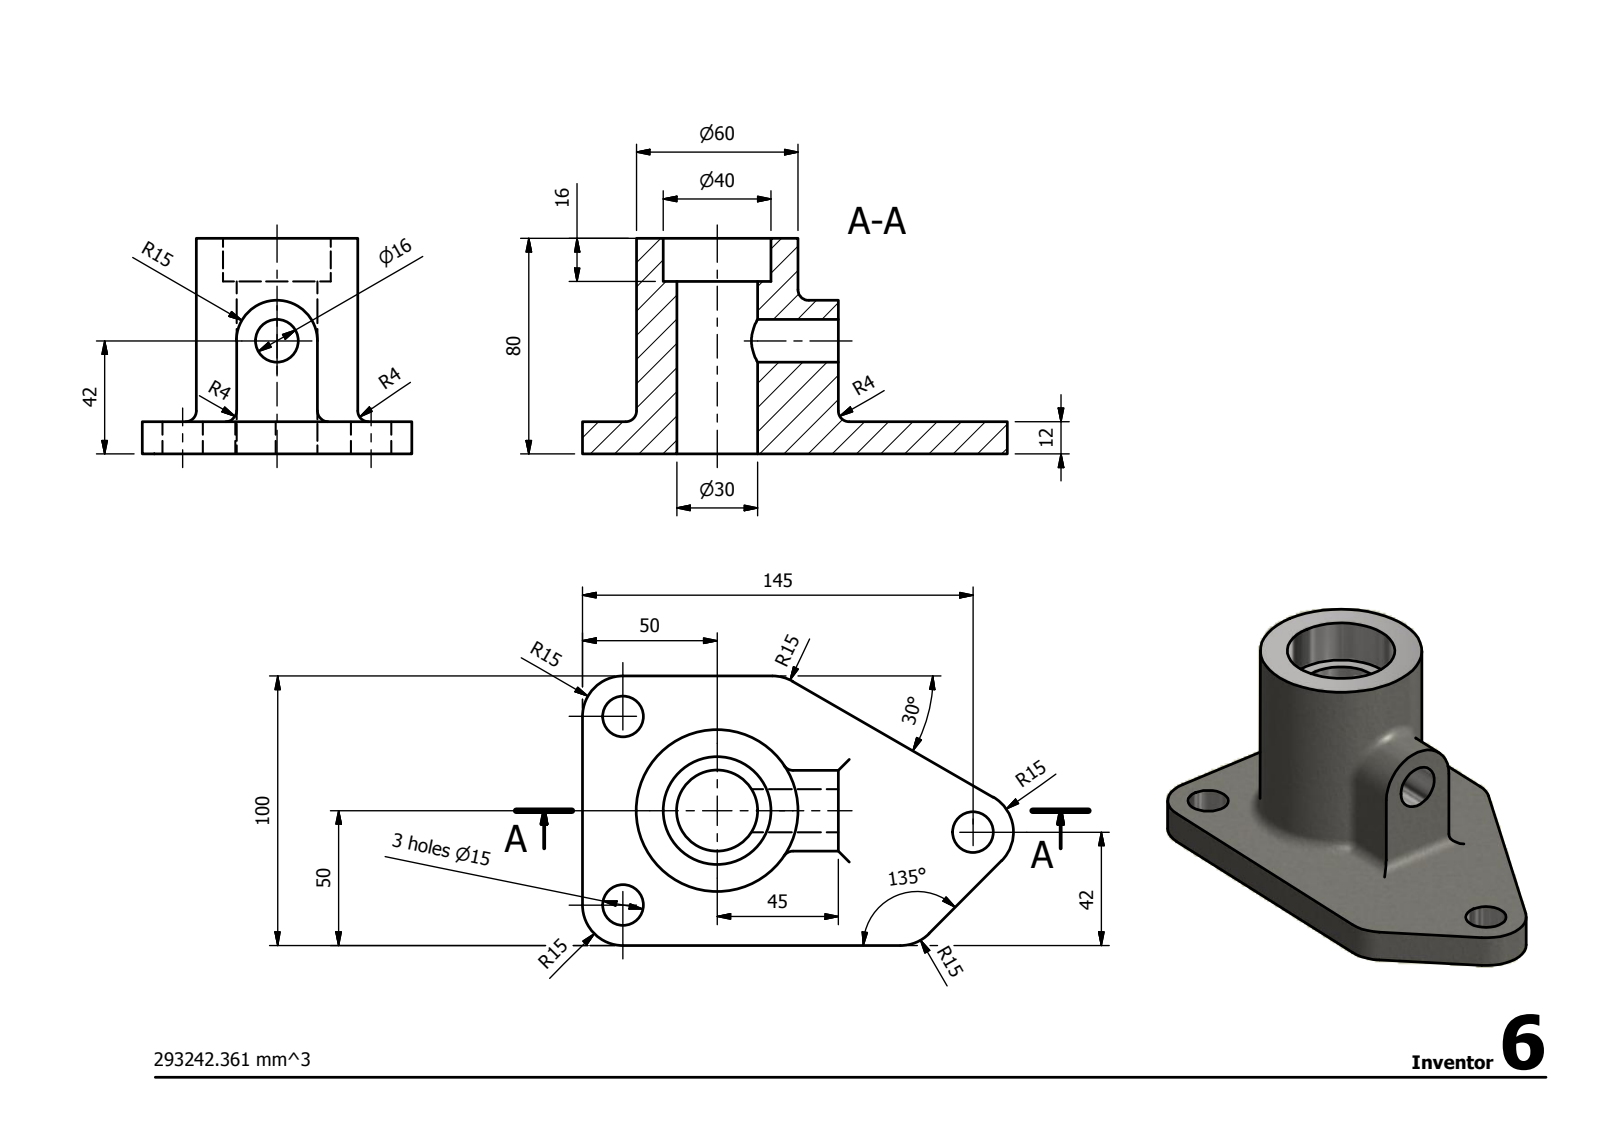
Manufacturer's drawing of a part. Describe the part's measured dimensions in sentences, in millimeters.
Its 3-D file was written by "Autodesk Inventor 2014 (AUTOMOTIVE_DESIGN)". It is 1 solid with 34 faces: 12 planar, 18 cylindrical and 4 other. Overall it measures 160 by 100 by 80 millimeters. Its volume is 293 243 cubic millimeters and its surface area 53 817 square millimeters. Round holes: 3 of diameter 15, 1 of diameter 16, 1 of diameter 30, 1 of diameter 40. Round bosses or shafts: 1 of diameter 60. Partial cylindrical surfaces (rounded edges, fillets, slot ends): 6 of radius 15, 5 of radius 4. The main face-to-face distances are 12, 80, 68, 35, 65, 95, 100, 64, 52, 16. The hole center spacings are 49.5, 70, 95.34, 132.77, 136.93.
